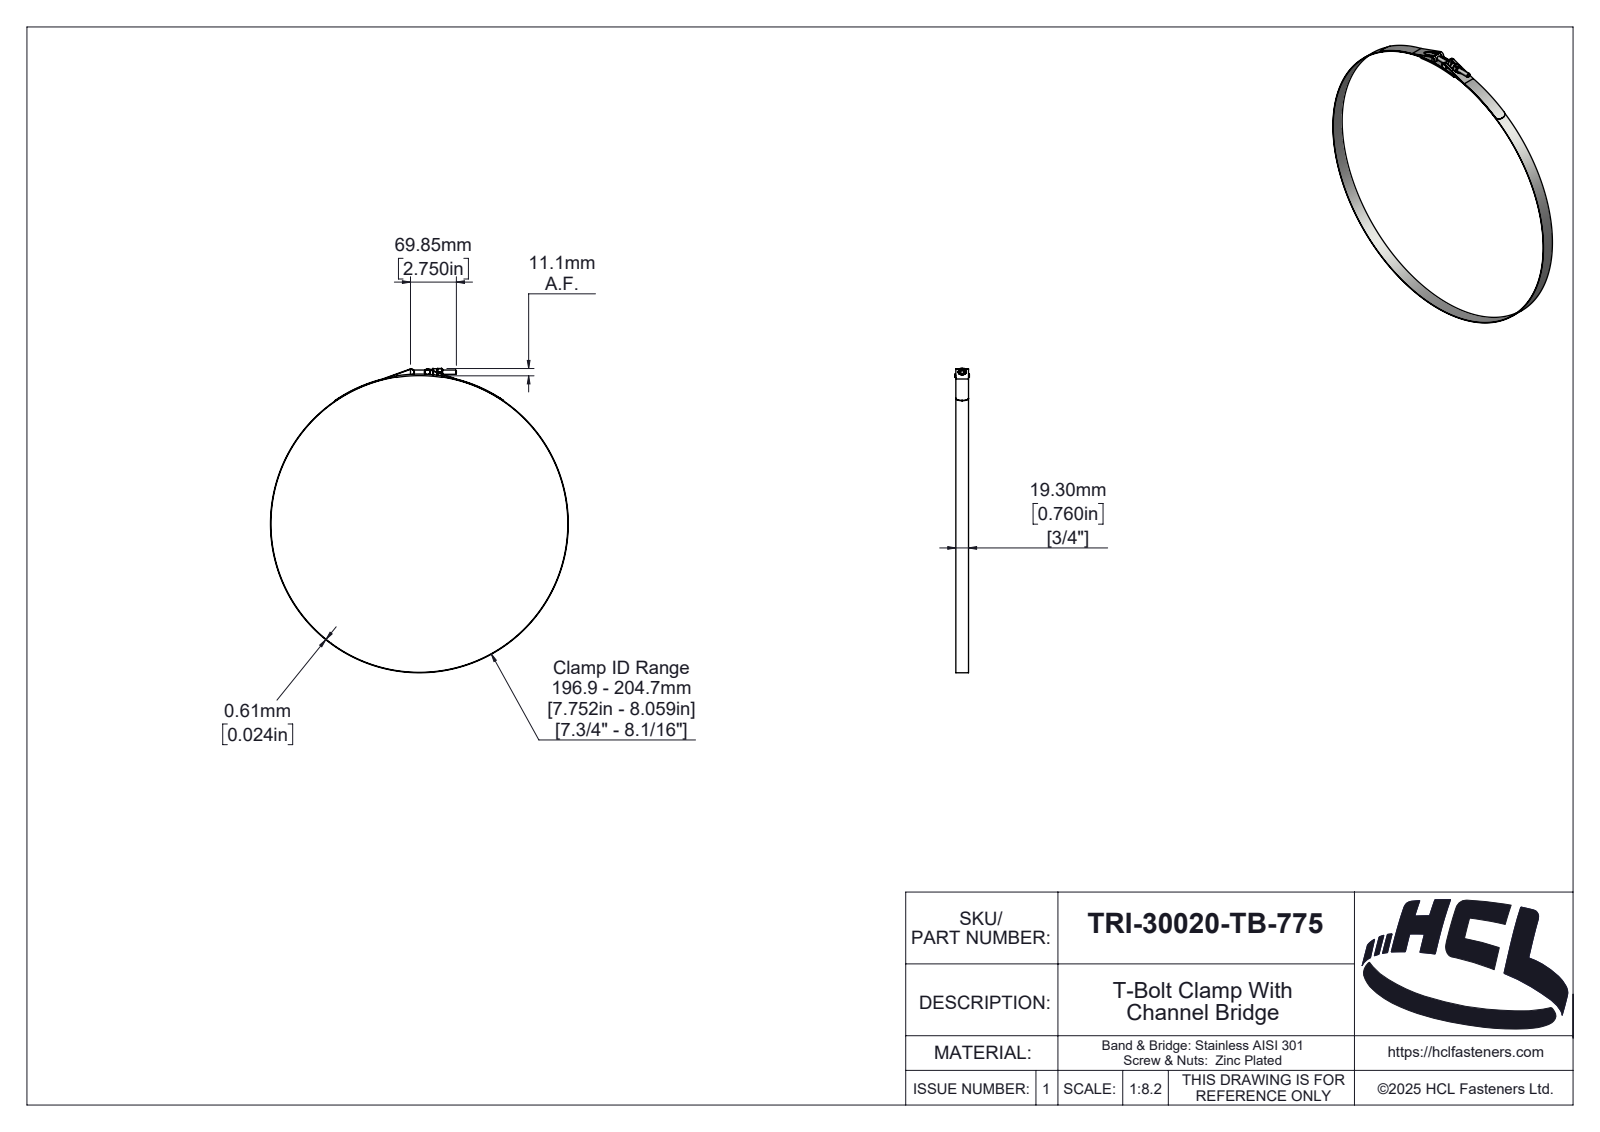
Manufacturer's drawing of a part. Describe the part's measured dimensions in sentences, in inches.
The part is named "TRI-30020-TB-775". Its 3-D file was written by "SolidWorks 2025 (AUTOMOTIVE_DESIGN)". It is 6 solids with 330 faces: 44 planar, 122 cylindrical and 164 other. Overall it measures 18.228 by 17.843 by 0.866 inches. Its volume is 1.495 cubic inches and its surface area 113.5 square inches. Round holes: 1 of diameter 0.213, 1 of diameter 0.25, 1 of diameter 0.256, 1 of diameter 0.298, 1 of diameter 17.795. Round bosses or shafts: 2 of diameter 0.338, 1 of diameter 17.843, 1 of diameter 0.417. Partial cylindrical surfaces (rounded edges, fillets, slot ends): 6 of radius 0.015, 2 of radius 0.02, 2 of radius 0.173, 2 of radius 0.197, 1 of radius 0.023, 1 of radius 0.095, 1 of radius 0.119, 1 of radius 0.126. The main face-to-face distances are 0.024, 0.76, 0.053, 0.813, 0.029, 0.842, 0.789, 0.866, 0.818, 1.614. The hole center spacings are 9.094.
